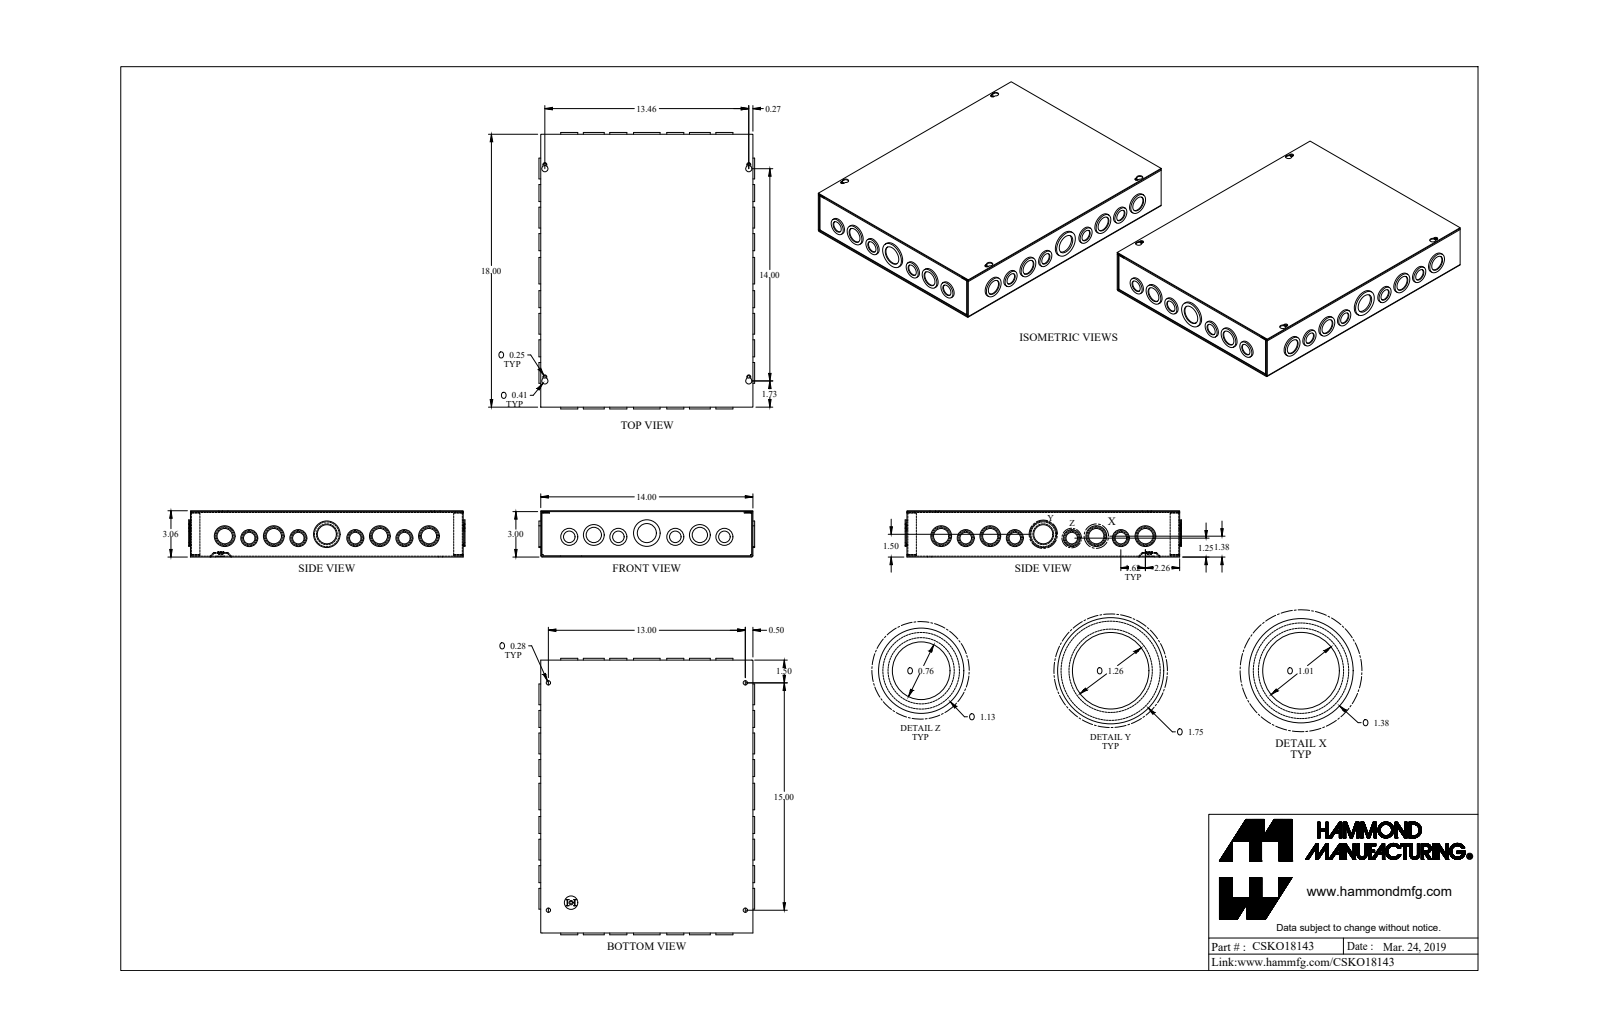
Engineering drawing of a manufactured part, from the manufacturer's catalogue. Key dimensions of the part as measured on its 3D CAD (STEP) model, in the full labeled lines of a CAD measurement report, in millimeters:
Part name (STEP PRODUCT): CSKO18143_Default
STEP written by: SolidWorks 2019 (CONFIG_CONTROL_DESIGN)
Units: millimetres
Bodies: 4 solids, 589 faces (253 planar, 328 cylindrical, 8 other)
Overall size (bounding box): 463.1 × 361.5 × 77.6
Volume: 706 800 mm³ · Surface area: 985 200 mm²
Round holes (diameter × count): ⌀25.7 ×14, ⌀19.3 ×8, ⌀32 ×8, ⌀4.3 ×5, ⌀7.1 ×4, ⌀41.6 ×2, ⌀12.7 ×1
Round bosses / shafts (diameter × count): ⌀28.6 ×12, ⌀22.2 ×8, ⌀34.9 ×7, ⌀28.6 ×4, ⌀44.5 ×2, ⌀22.2 ×2, ⌀34.9 ×1, ⌀12.5 ×1
Partial cylindrical surfaces — rounded edges, fillets, slot ends (radius × count): R0.7 ×12, R2.2 ×12, R1.4 ×8, R3.2 ×4, R5.2 ×4
Main face-to-face distances: 1.4, 76.2, 74.8, 77.6, 354.2, 455.8, 355.6, 457.2, 2.9, 352.7
Hole centre spacings: 41.3, 82.3, 177.8, 219, 14, 48.2, 89, 130.2
